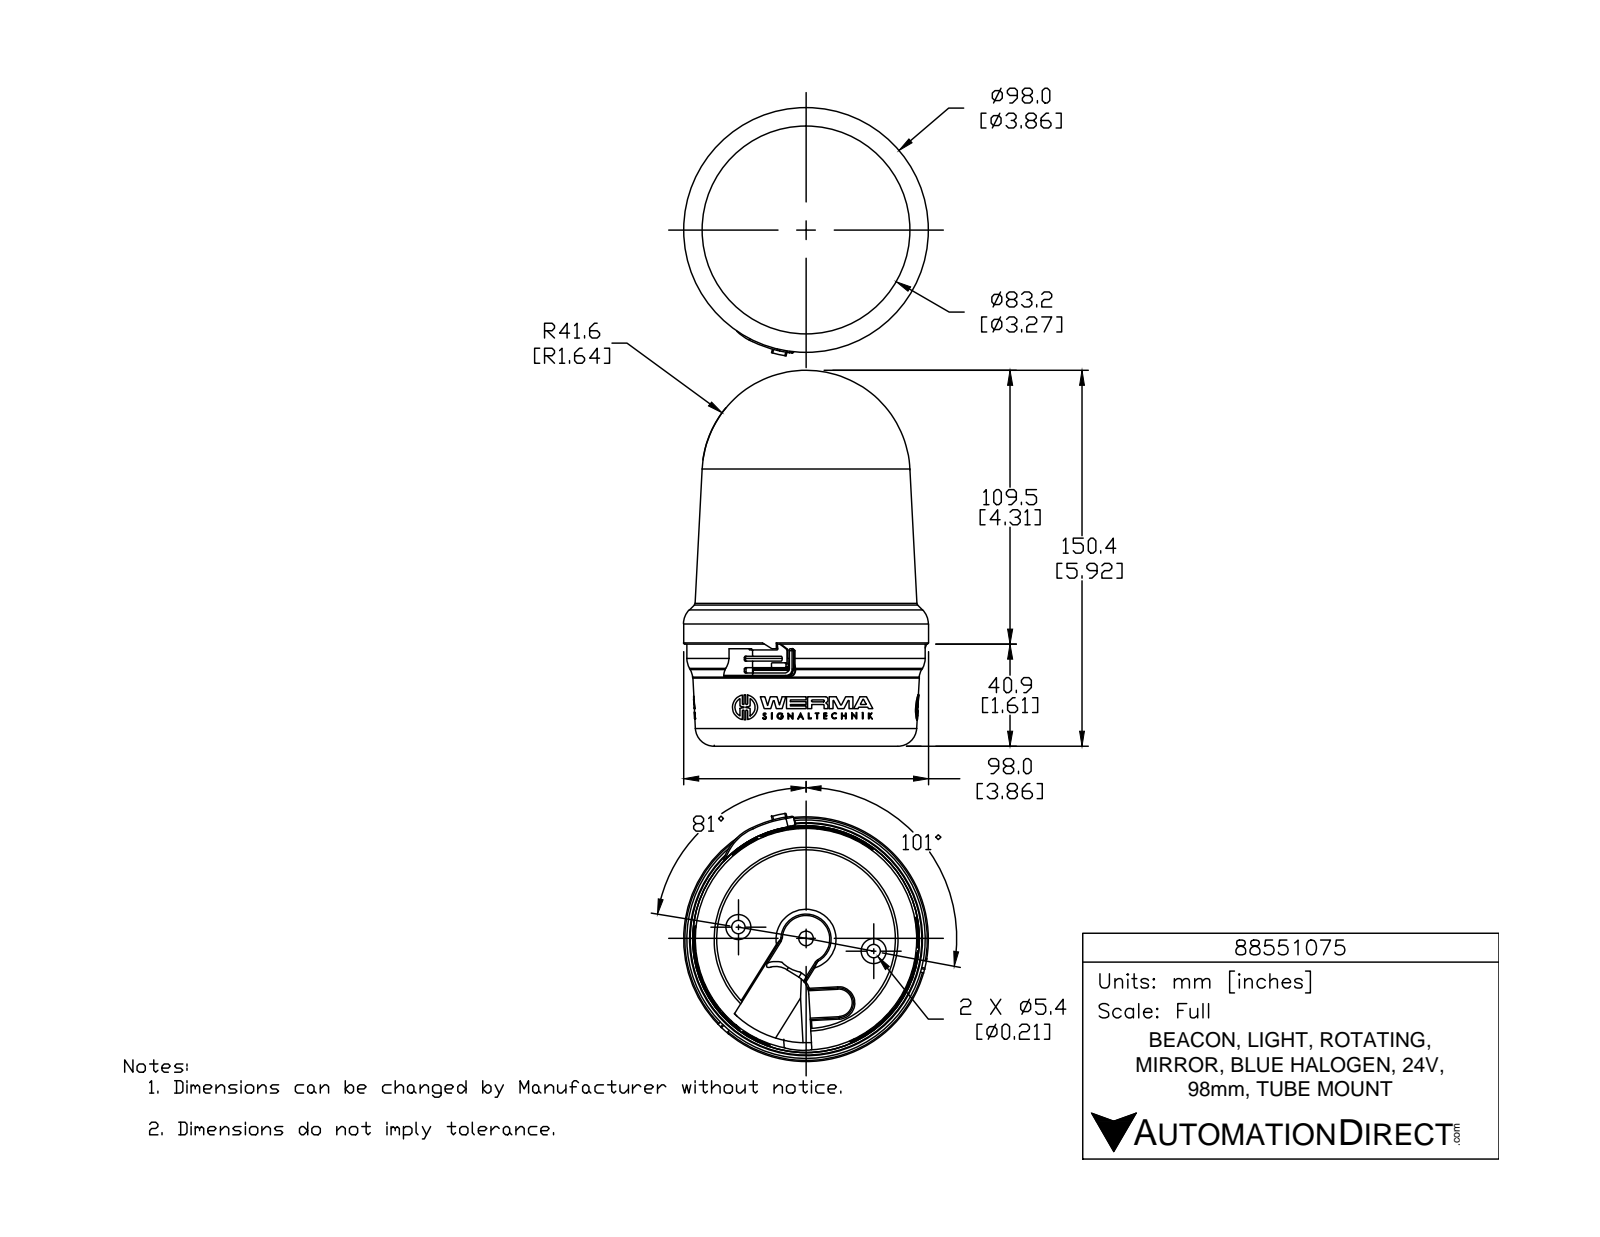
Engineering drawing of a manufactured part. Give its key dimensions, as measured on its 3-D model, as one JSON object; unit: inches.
{"part_name": "88551075", "step_written_by": "SolidWorks 2015 (AUTOMOTIVE_DESIGN)", "units": "inches", "bodies": {"solids": 1, "faces": 1006, "planar": 554, "cylindrical": 189, "other": 263}, "overall_size": [7.914, 3.912, 3.858], "volume_in3": 54.7, "surface_area_in2": 91.39, "round_holes": [[0.078, 3], [1.013, 1], [1.024, 1]], "round_bosses_or_shafts": [[0.452, 3], [0.113, 3], [3.858, 1], [1.409, 1], [1.261, 1]], "partial_cylinders_radius": [[0.02, 12], [0.007, 9], [0.007, 6], [0.016, 6], [0.016, 6], [0.016, 6], [0.262, 6], [0.006, 3]], "face_to_face_distances": [2.214, 0.462, 2.676, 0.335, 0.127, 2.548, 2.603, 2.476, 2.141, 0.073]}
